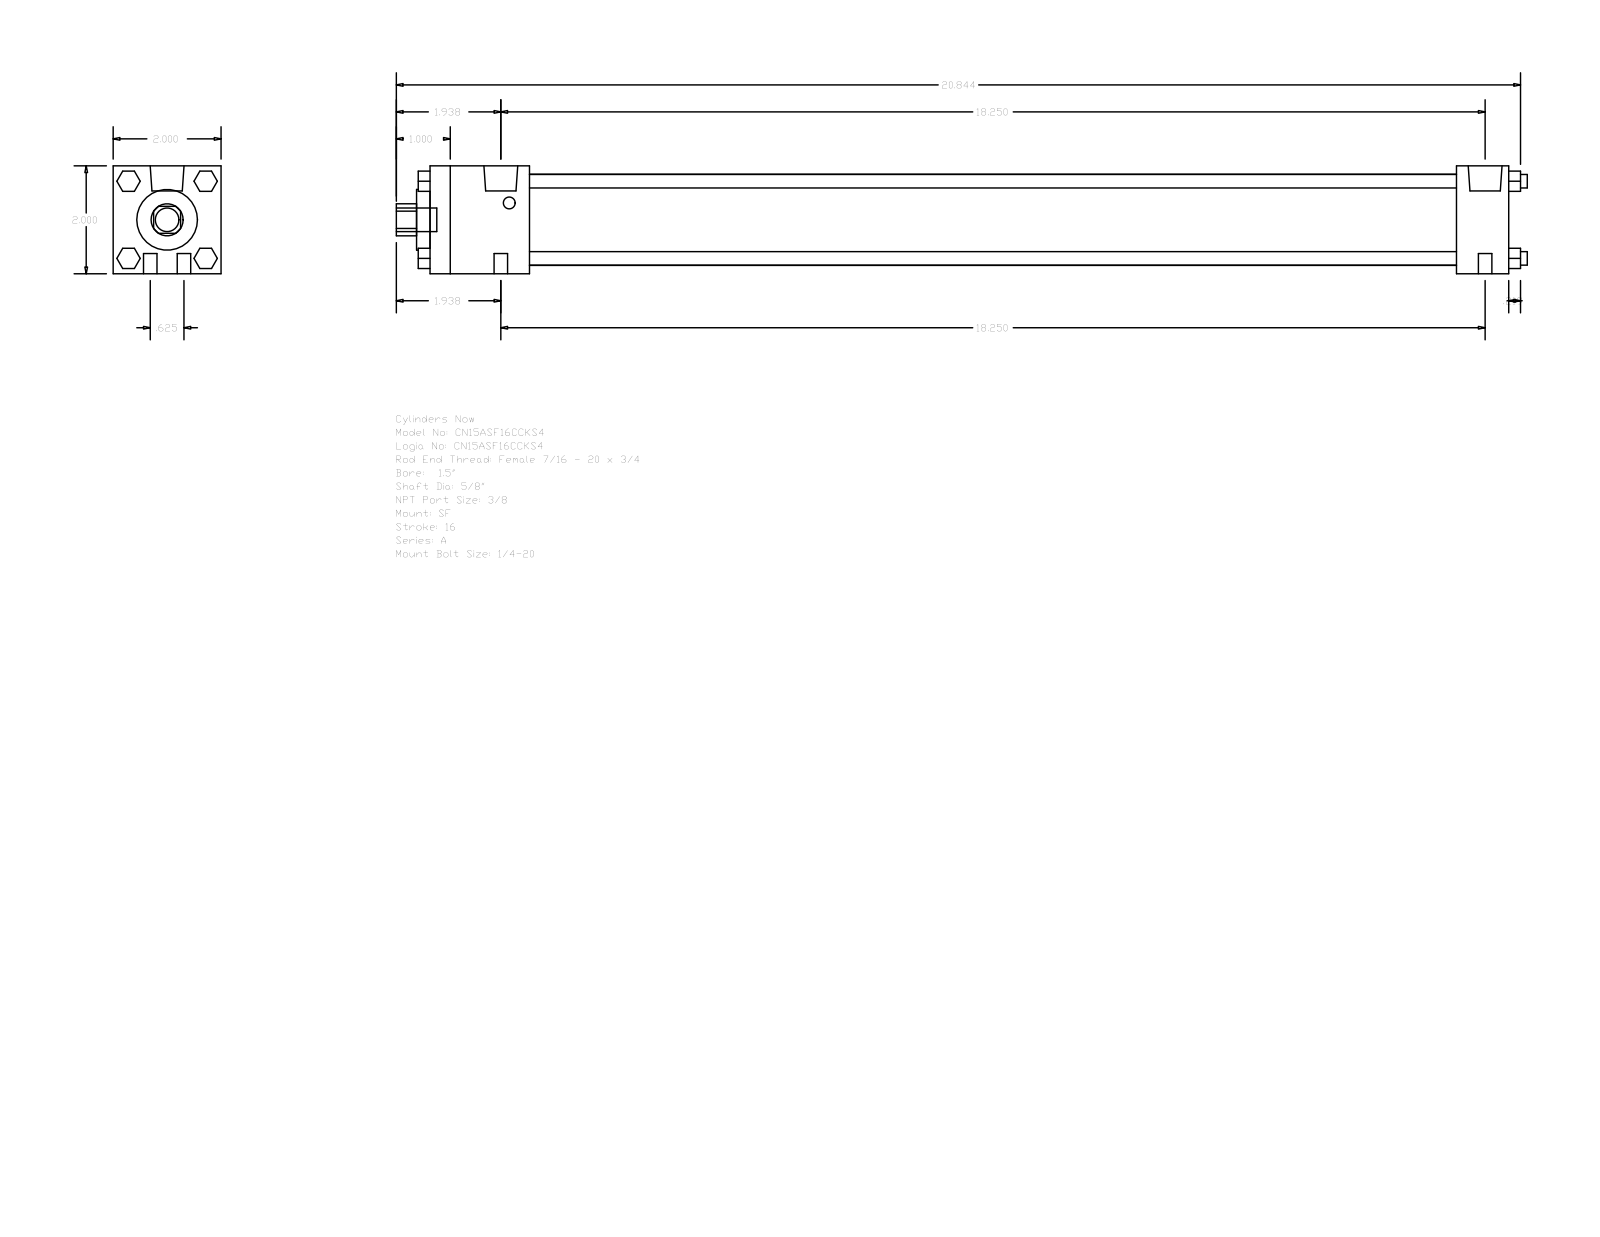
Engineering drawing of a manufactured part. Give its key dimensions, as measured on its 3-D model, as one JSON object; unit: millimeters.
{"part_name": "A_SF__0150_0.625", "step_written_by": "GSSL Pune (CONFIG_CONTROL_DESIGN)", "units": "millimeters", "bodies": {"solids": 0, "faces": 124, "planar": 94, "cylindrical": 30, "other": 0}, "overall_size": [532.61, 50.8, 50.8], "round_holes": [[15.88, 1], [28.57, 1], [42.93, 1]], "round_bosses_or_shafts": [[6.35, 8], [15.93, 2], [5.56, 2], [11.11, 1]], "partial_cylinders_radius": [[7.54, 1]], "face_to_face_distances": [50.8, 508, 46.83, 483.39, 436.56, 461.17, 24.61, 9.52, 6.35, 53.18]}
